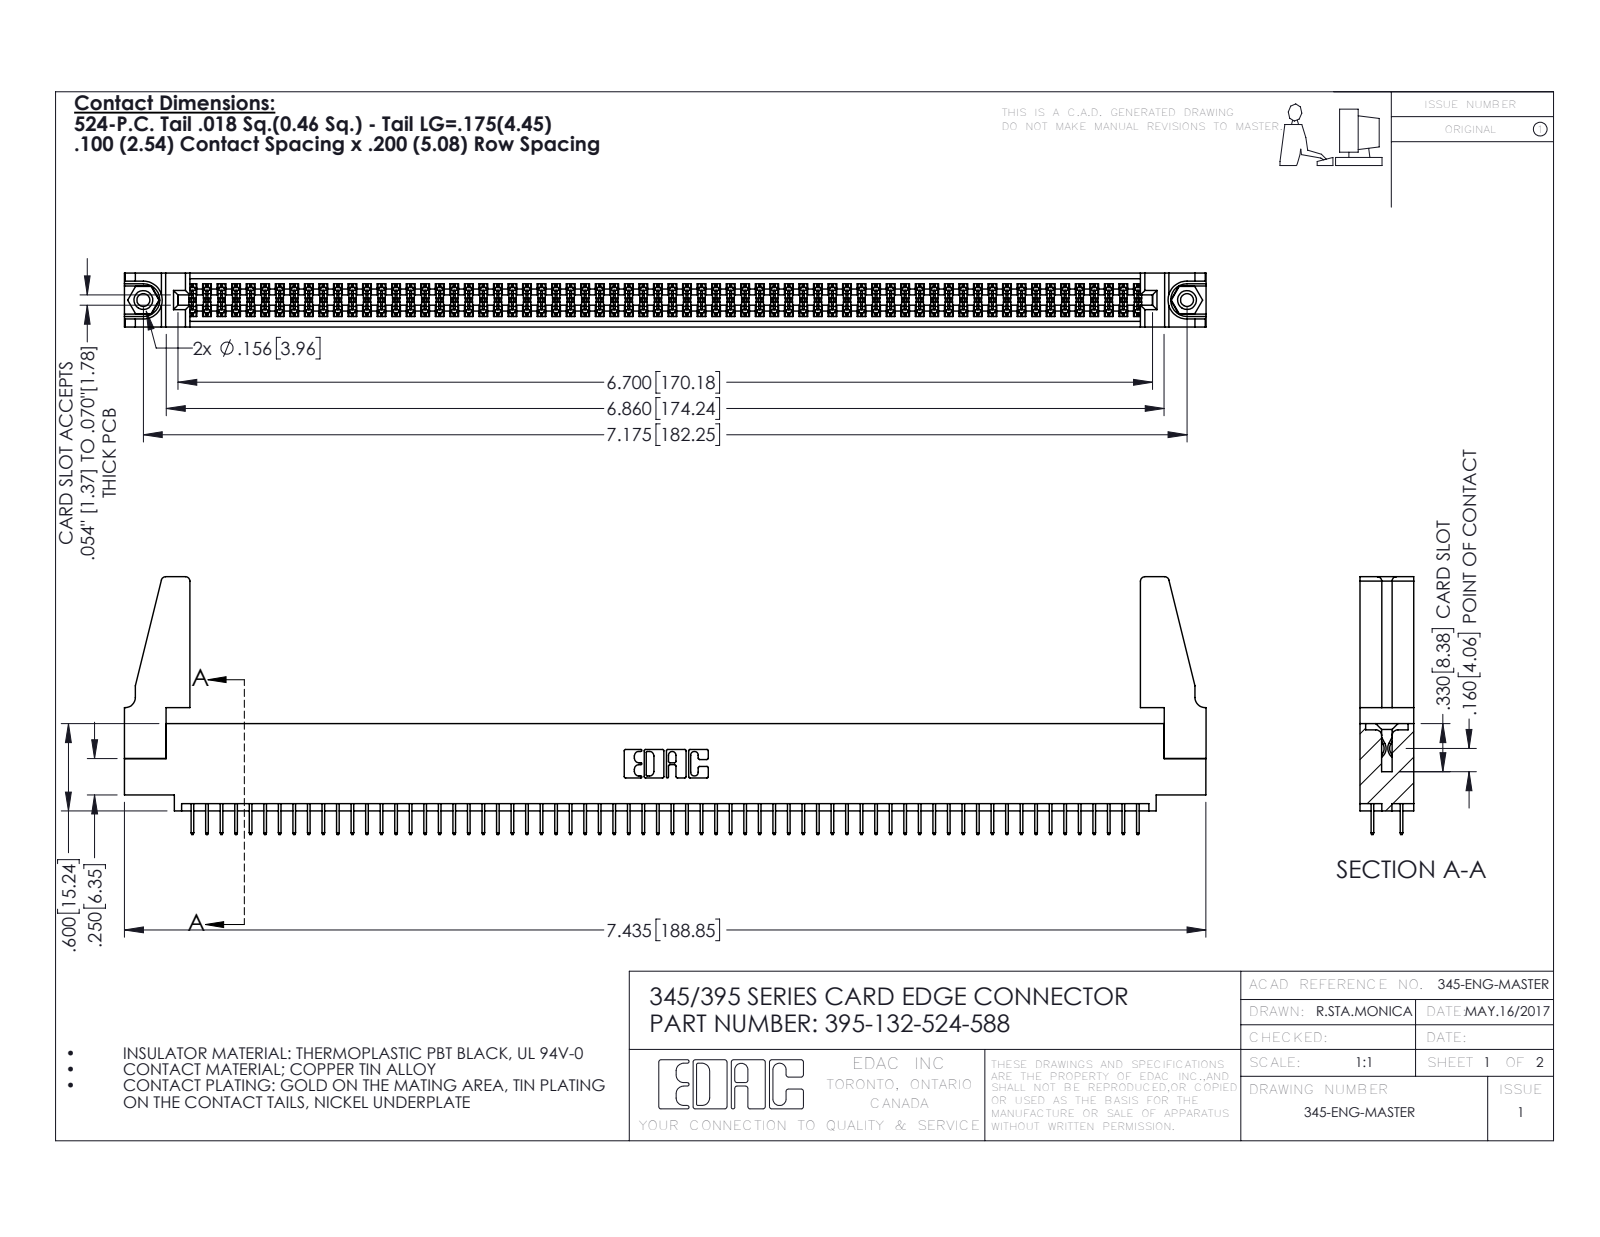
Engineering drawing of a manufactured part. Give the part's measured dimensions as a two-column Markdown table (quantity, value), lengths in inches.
| quantity | value |
| --- | --- |
| part name | 345-250-001_345-250-001-102; 395-132-524-588; 345-220-078_345-220-088; 345-292-001_345-293-124 (+1 more) |
| STEP written by | SolidWorks 2016 (CONFIG_CONTROL_DESIGN) |
| units | inches |
| bodies | 137 solids, 7382 faces (5304 planar, 2062 cylindrical, 16 other) |
| overall size | 7.436 × 1.772 × 0.37 |
| volume | 1.315 in³ |
| surface area | 46.81 in² |
| round holes (diameter × count) | 0.089 × 2, 0.125 × 2, 0.156 × 2, 0.064 × 1 |
| round bosses / shafts (diameter × count) | 0.155 × 2 |
| partial cylindrical surfaces (radius × count) | 0.006 × 198, 0.01 × 22, 0.03 × 8, 0.007 × 6, 0.031 × 6, 0.026 × 3, 0.014 × 2, 0.019 × 2 |
| main face-to-face distances | 0.072, 0.298, 0.37, 0.2, 0.098, 0.272, 0.025, 0.225, 0.072, 0.175 |
| hole center spacings | 0.27, 6.939, 7.175 |
